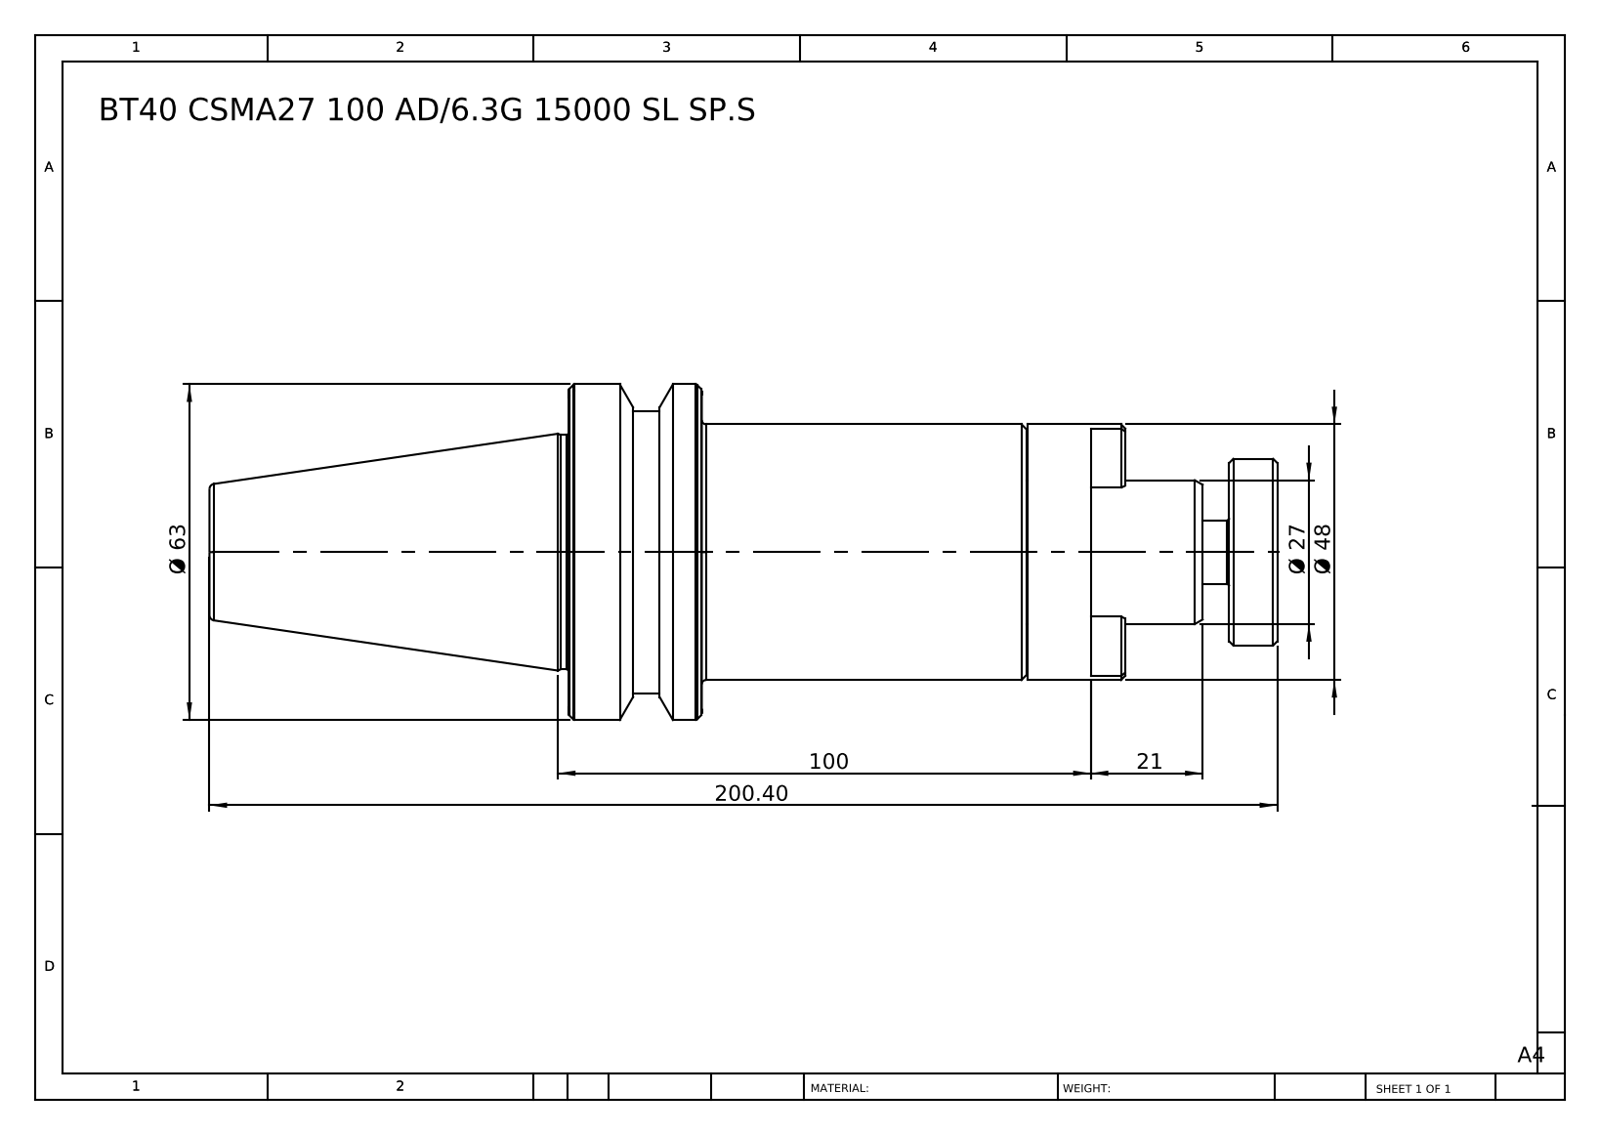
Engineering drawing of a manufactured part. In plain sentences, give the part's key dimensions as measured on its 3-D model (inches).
The part is named "BT40 CSMA27 100 AD-6.3G 15000 SL SP". Its 3-D file was written by "SolidWorks 2014 (CONFIG_CONTROL_DESIGN)". It is 2 solids with 87 faces: 22 planar, 20 cylindrical and 45 other. Overall it measures 7.89 by 2.48 by 2.48 inches. Its volume is 17.88 cubic inches and its surface area 60.04 square inches. Round holes: 1 of diameter 1.063. Round bosses or shafts: 1 of diameter 2.48, 1 of diameter 2.087, 1 of diameter 1.89, 1 of diameter 1.732, 1 of diameter 1.378, 1 of diameter 0.472. The main face-to-face distances are 3.393, 0.472, 3.386, 0.465, 3.858, 2.874, 2.409, 2.402, 0.984, 1.378.
